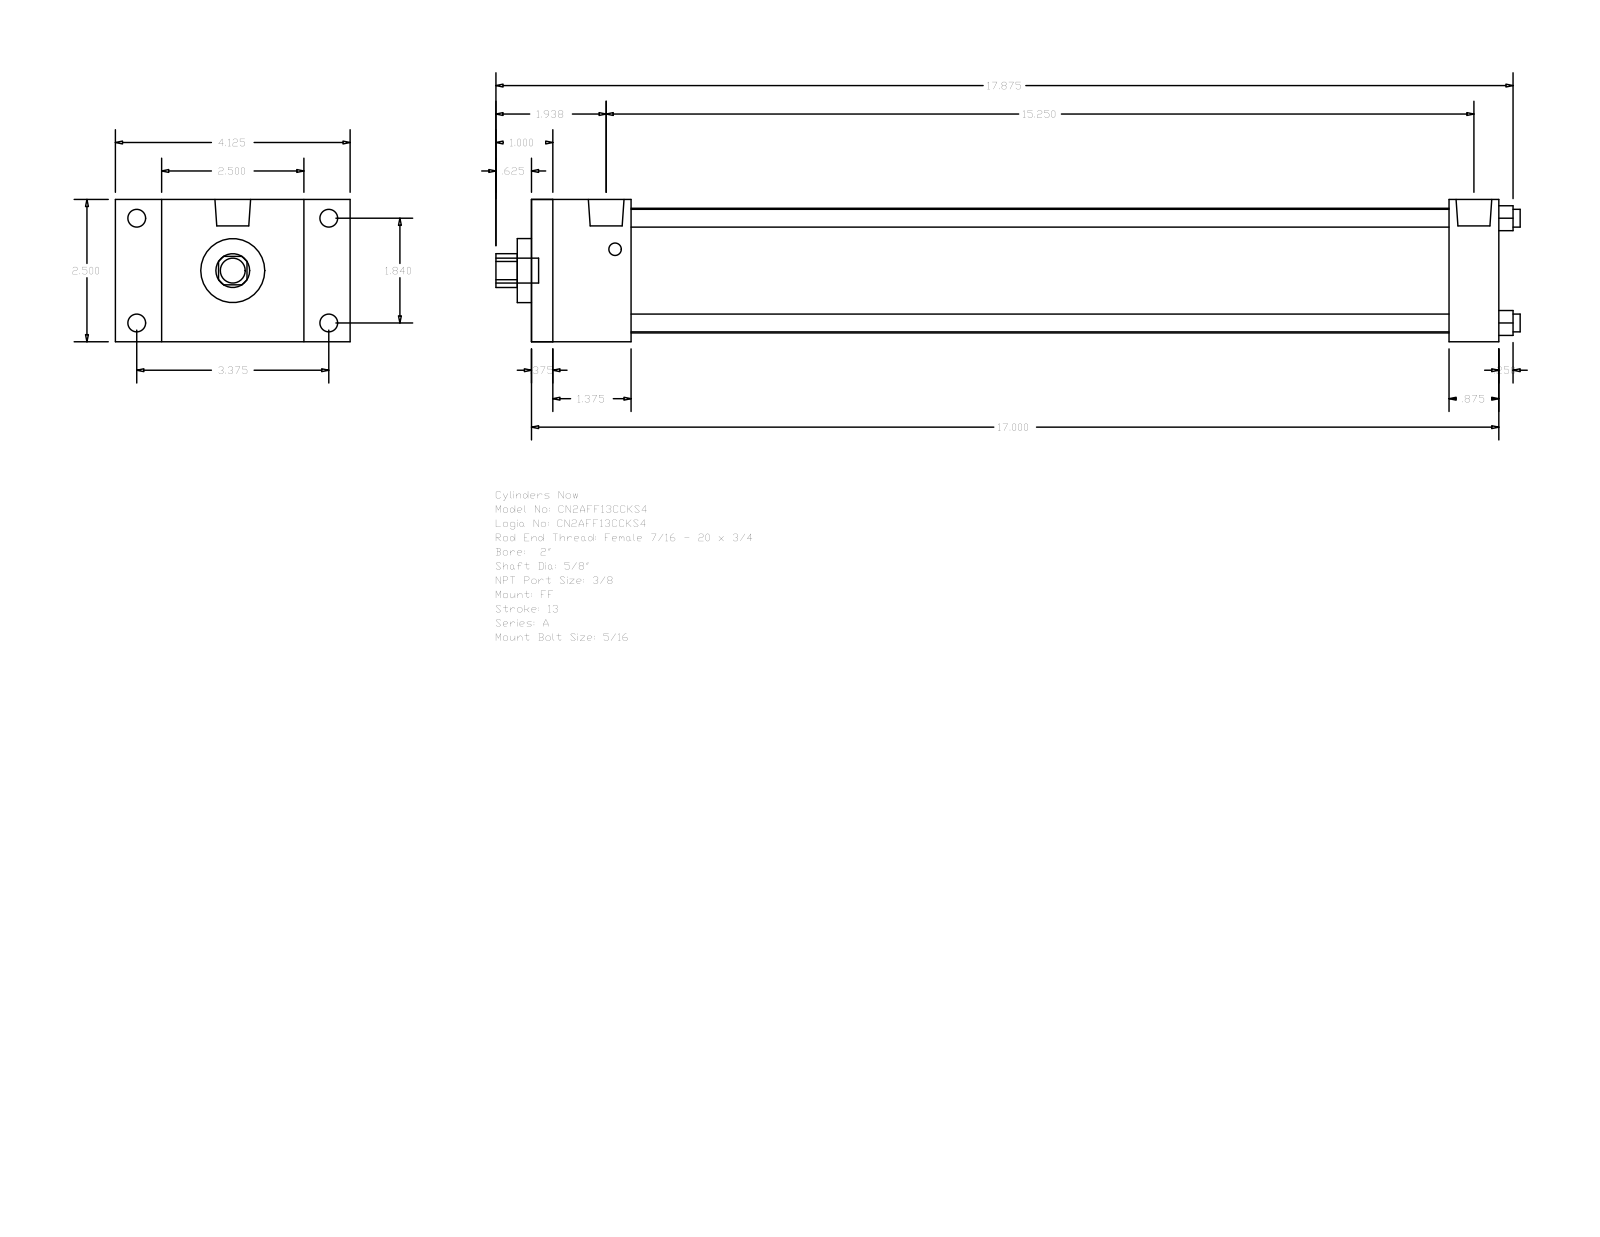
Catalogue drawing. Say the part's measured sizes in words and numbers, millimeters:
The part is named "A_FF__0200_0.625". Its 3-D file was written by "GSSL Pune (CONFIG_CONTROL_DESIGN)". It is 0 solids with 92 faces: 64 planar, 28 cylindrical and 0 other. Overall it measures 457.2 by 104.78 by 63.5 millimeters. Round holes: 4 of diameter 7.94, 1 of diameter 15.88, 1 of diameter 28.57, 1 of diameter 55.63. Round bosses or shafts: 4 of diameter 7.94, 4 of diameter 5.56, 2 of diameter 15.93, 1 of diameter 11.11. Partial cylindrical surfaces (rounded edges, fillets, slot ends): 1 of radius 7.54. The main face-to-face distances are 63.5, 431.8, 9.52, 422.28, 44.45, 409.57, 34.93, 400.05, 365.12, 387.35. The hole center spacings are 33.05, 46.74, 66.1.
